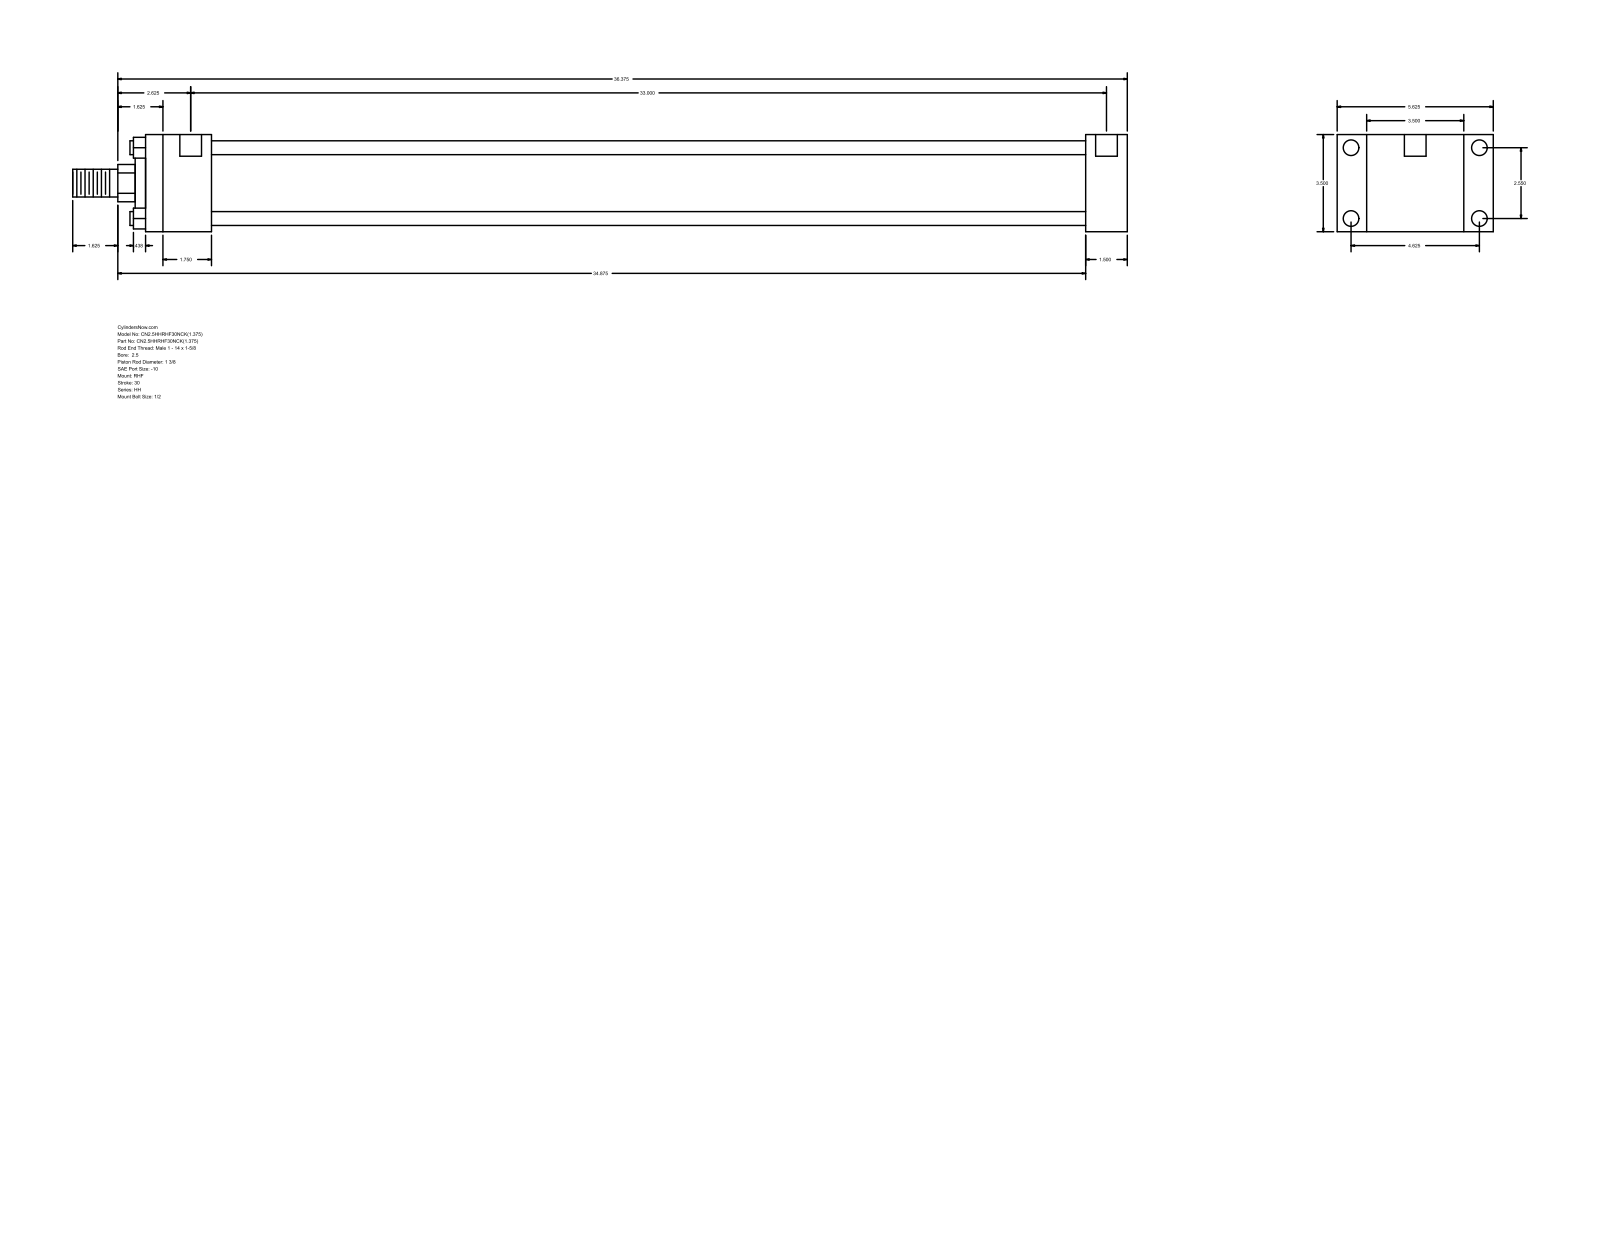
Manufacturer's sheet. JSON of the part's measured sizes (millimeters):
{"part_name": "HH_RHF__0250_1.375", "step_written_by": "GSSL Pune (CONFIG_CONTROL_DESIGN)", "units": "millimeters", "bodies": {"solids": 0, "faces": 88, "planar": 60, "cylindrical": 28, "other": 0}, "overall_size": [965.2, 142.88, 88.9], "round_holes": [[5.56, 4], [14.3, 4], [19.84, 2]], "round_bosses_or_shafts": [[12.7, 4], [73.03, 1], [50.8, 1], [34.92, 1], [25.4, 1]], "partial_cylinders_radius": [[17.06, 1]], "face_to_face_distances": [88.9, 38.09, 26.99, 115.89, 860.43, 898.52, 142.88, 60.32, 800.11, 838.2], "hole_center_spacings": [1.58, 64.76, 117.48, 134.15, 839.79, 841.37, 838.21]}
